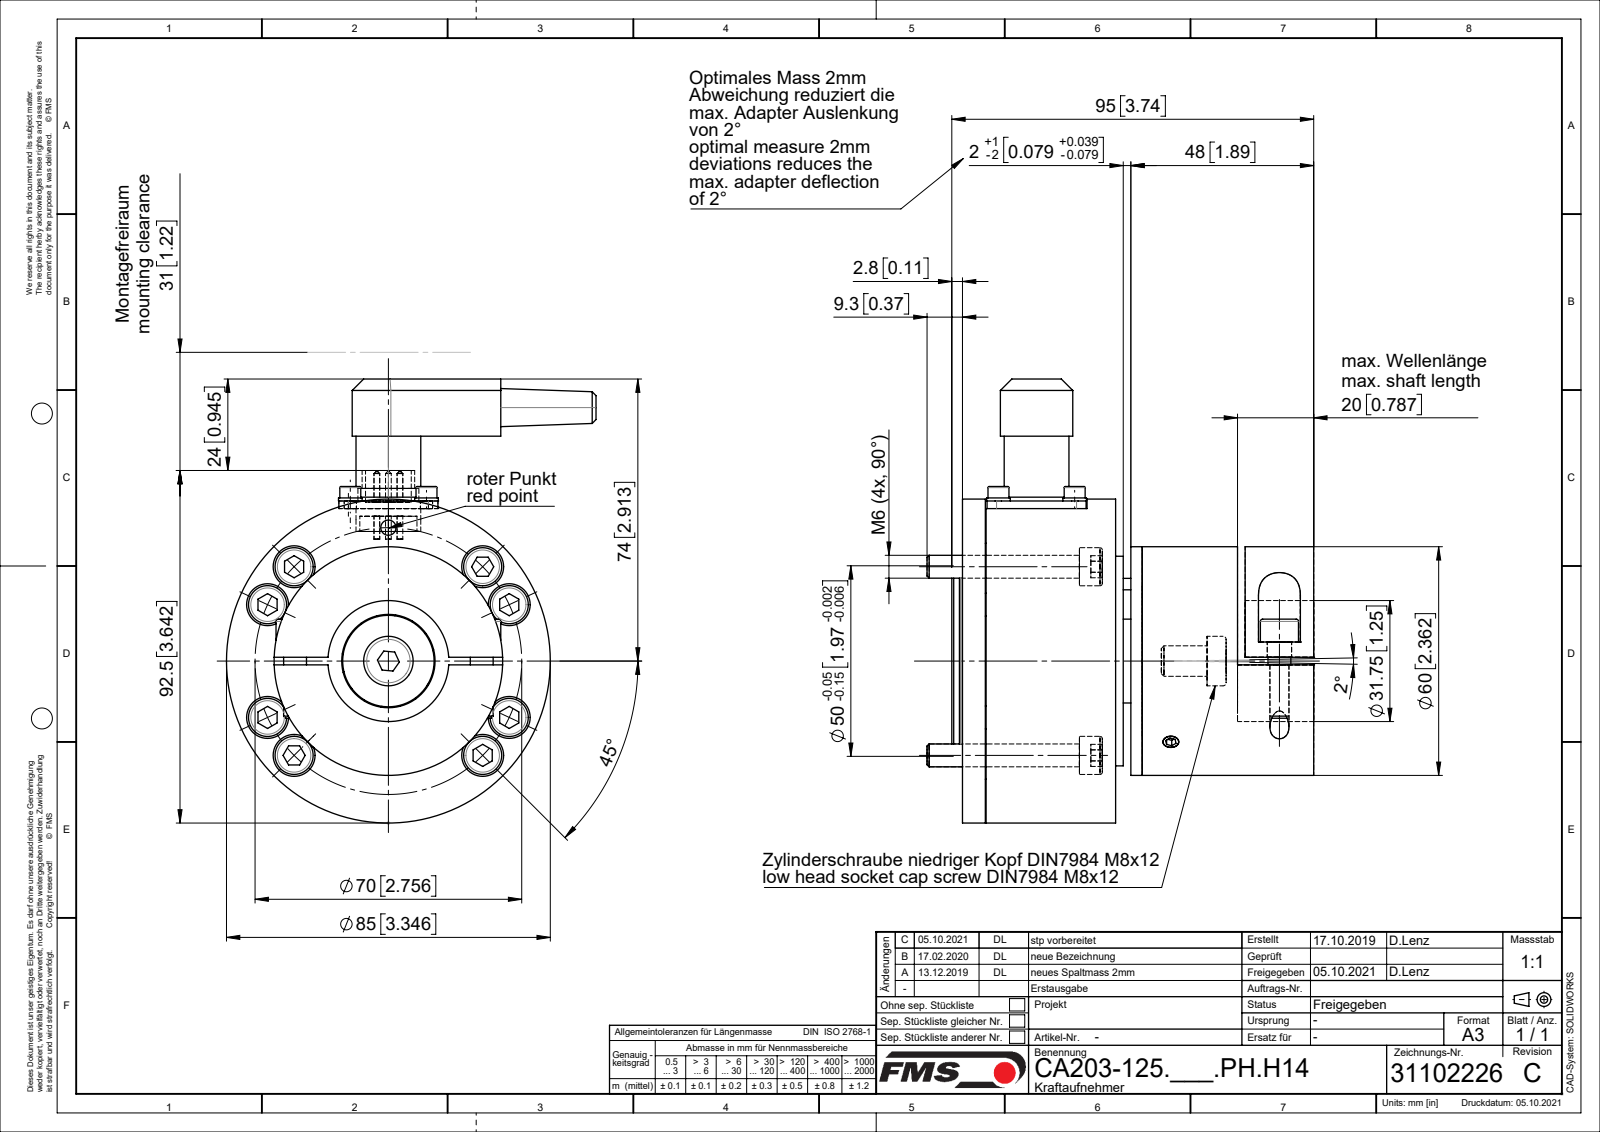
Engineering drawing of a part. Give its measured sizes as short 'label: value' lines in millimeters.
name: Federringe_DIN127A_M03; 31100948_01; Zyl-Schr DIN912_M6x20; Se-Schr DIN7991_M3x8 (+8 more)
written by: SolidWorks 2018 (CONFIG_CONTROL_DESIGN)
unit: mm
bodies: 44 solids, 839 faces (302 planar, 339 cylindrical, 198 other)
size: 116.5 × 101.5 × 97
volume: 299 739 mm³; area: 111 747 mm²
holes: 8× ⌀2.5, 8× ⌀6.5, 8× ⌀11, 6× ⌀5, 5× ⌀2, 5× ⌀4, 4× ⌀3.1, 4× ⌀3.2, 4× ⌀3.6, 4× ⌀7, 2× ⌀6.4, 1× ⌀3
bosses: 11× ⌀6, 10× ⌀10, 8× ⌀3, 5× ⌀1.5, 4× ⌀6.2, 4× ⌀5.7, 4× ⌀5.5, 1× ⌀85
rounds: 4× R2.5, 2× R5, 2× R5.5, 1× R9.5
face distances: 2, 41, 30, 6, 45, 10, 34, 3, 50, 15
hole spacings: 35, 20, 24.78, 25.2, 32.8, 51.14, 56.46, 6
